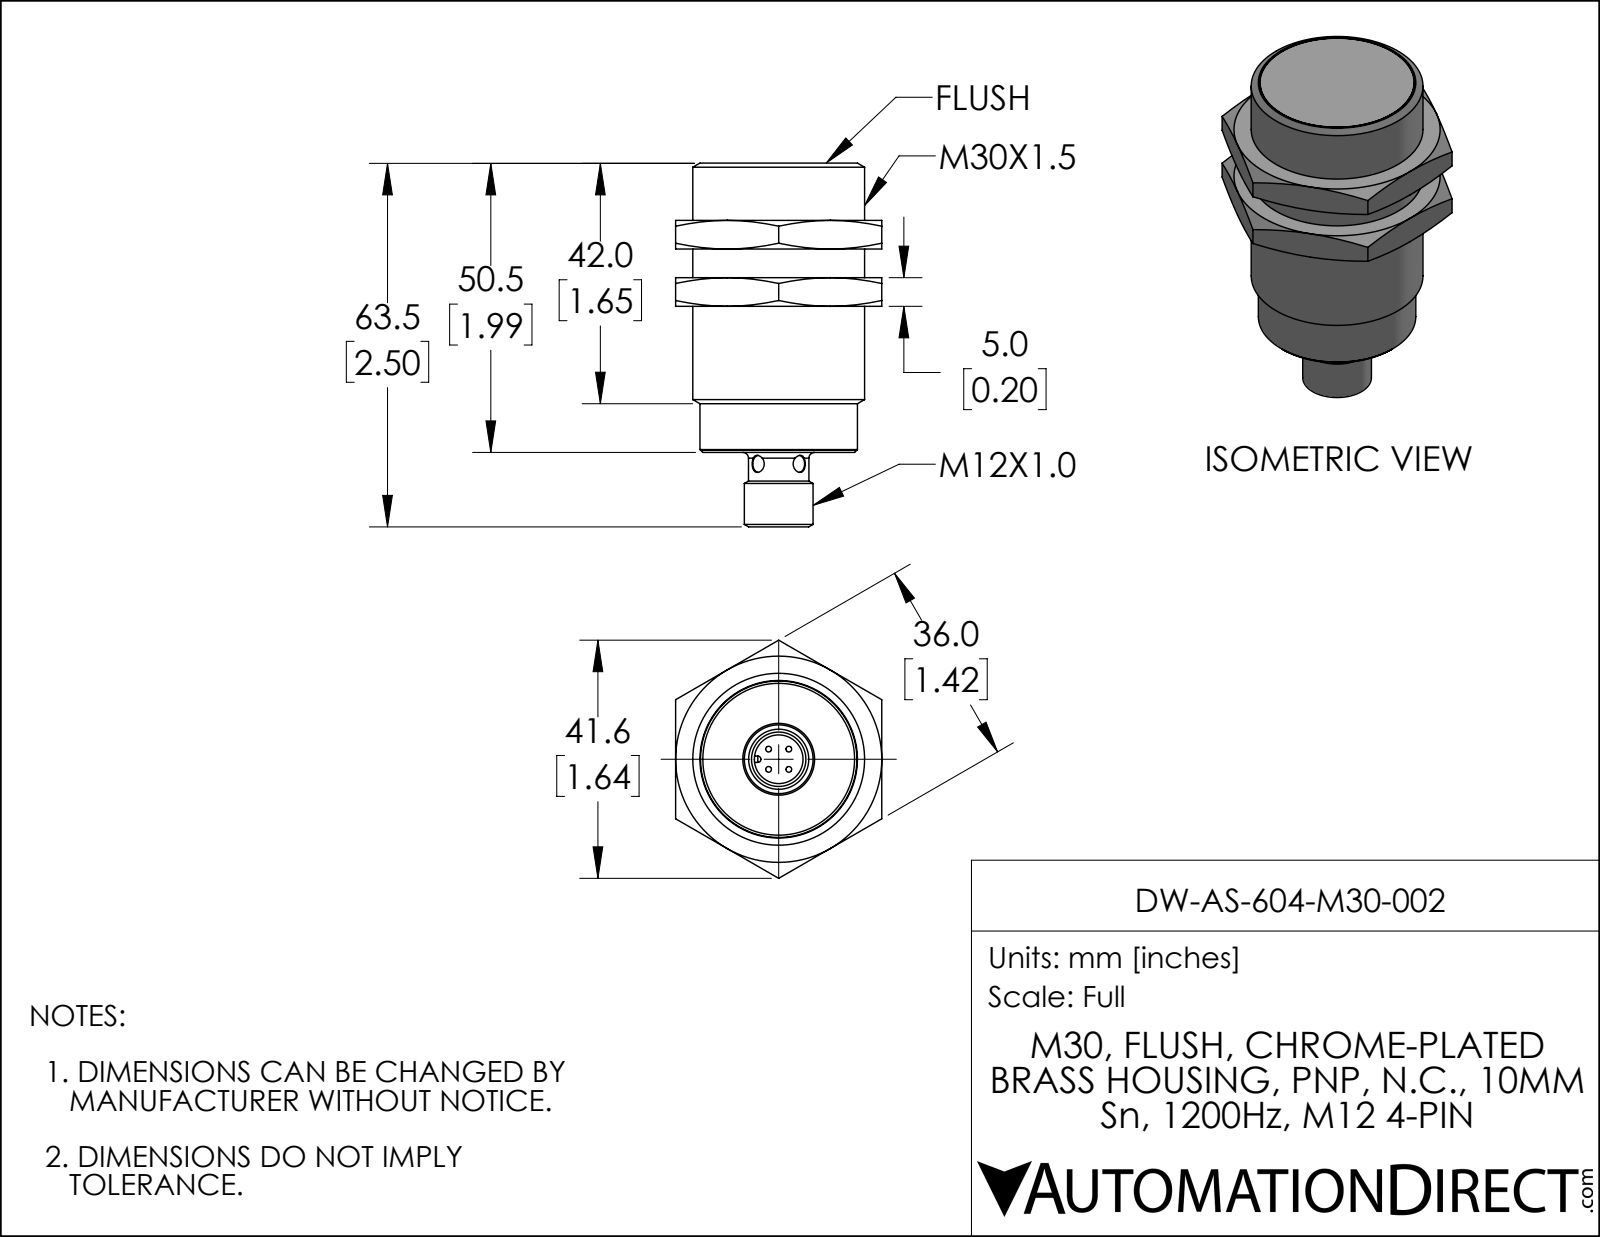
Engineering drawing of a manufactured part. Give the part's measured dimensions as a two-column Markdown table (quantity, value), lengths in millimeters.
| quantity | value |
| --- | --- |
| part name | DW-AS-604-M30-002 |
| STEP written by | SolidWorks 2019 (AUTOMOTIVE_DESIGN) |
| units | millimeters |
| bodies | 1 solid, 85 faces (29 planar, 20 cylindrical, 36 other) |
| overall size | 63.5 × 41.6 × 36 |
| volume | 39 530 mm³ |
| surface area | 8 626 mm² |
| round holes (diameter × count) | 3 × 2, 8.5 × 1, 27.1 × 1 |
| round bosses / shafts (diameter × count) | 1 × 4, 30 × 1, 27.5 × 1, 27.3 × 1, 26.9 × 1, 12 × 1, 10.5 × 1 |
| partial cylindrical surfaces (radius × count) | 0.6 × 2 |
| main face-to-face distances | 10, 5, 15, 36, 50.5, 25, 20, 40.5, 30.5, 25.5 |
